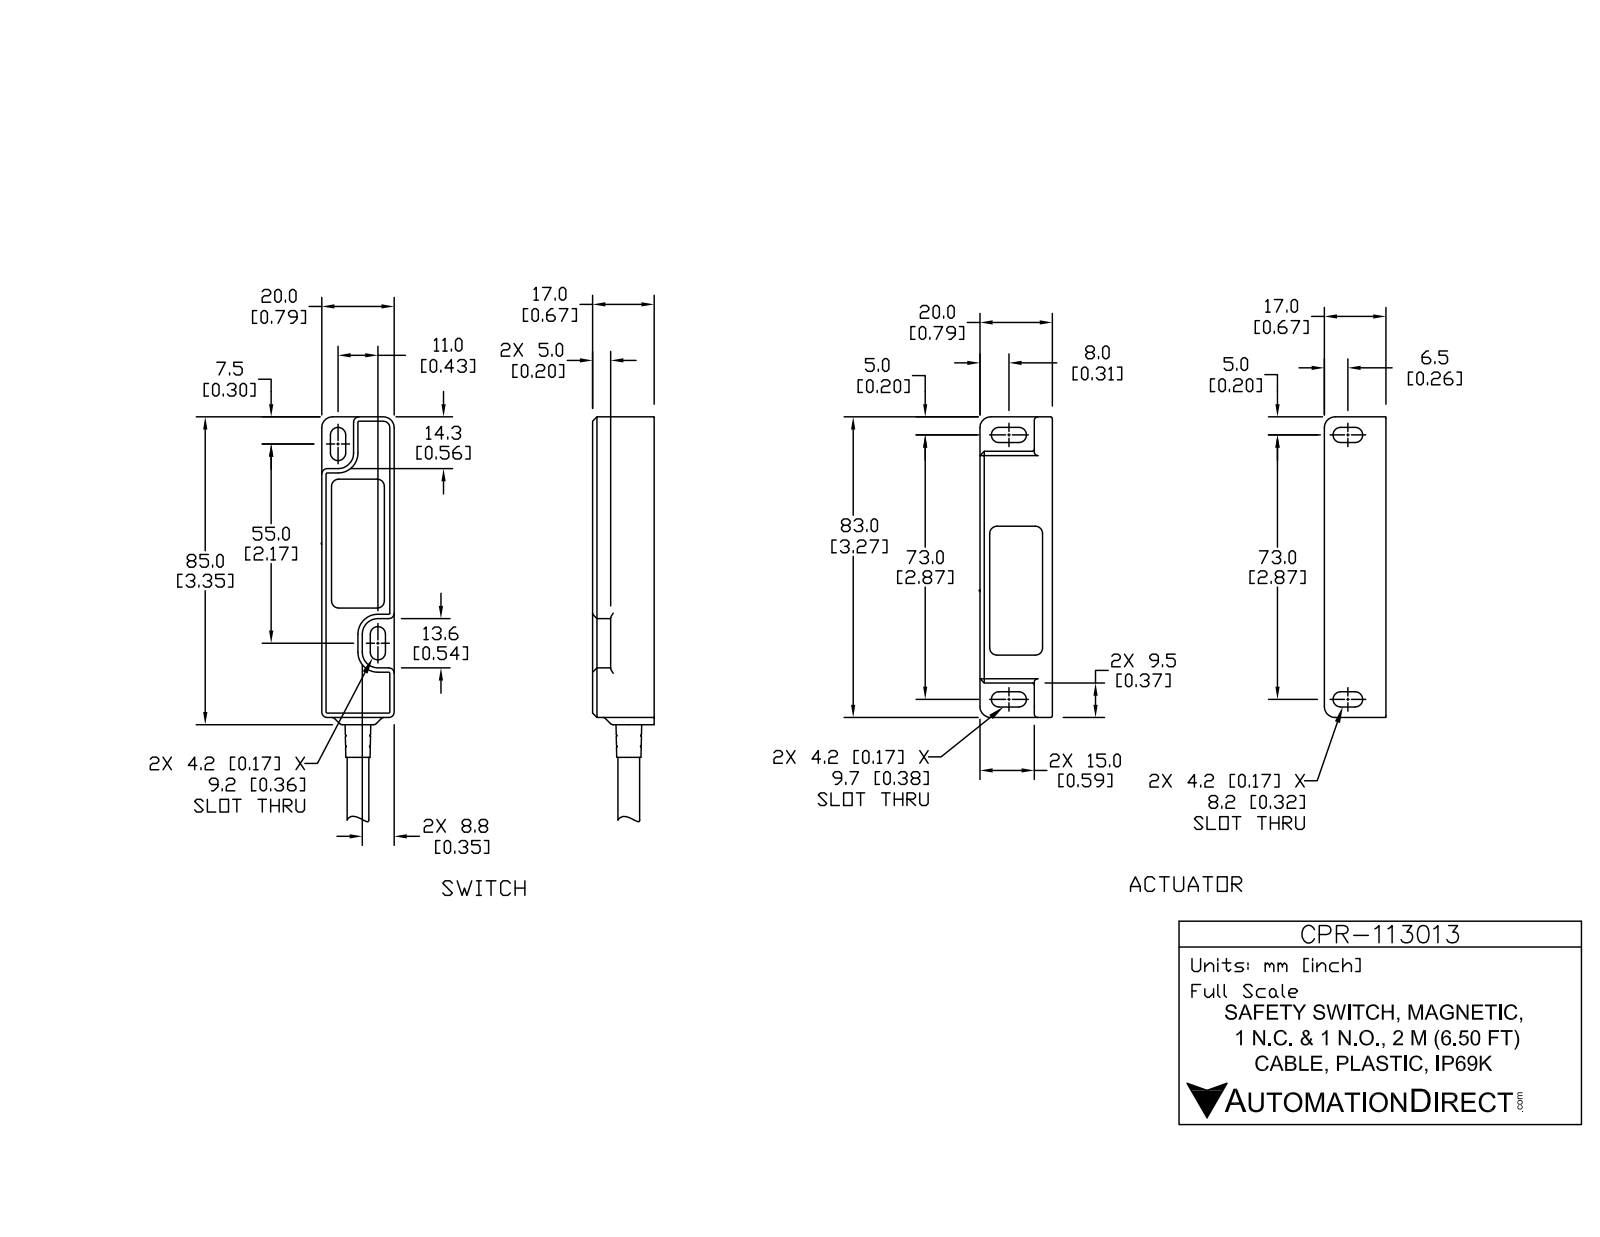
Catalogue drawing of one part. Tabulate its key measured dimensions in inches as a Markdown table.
| quantity | value |
| --- | --- |
| part name | CPR-113013; CPR-113013_1; CPR-113013_2 |
| STEP written by | SolidWorks 2017 (AUTOMOTIVE_DESIGN) |
| units | inches |
| bodies | 4 solids, 194 faces (77 planar, 69 cylindrical, 48 other) |
| overall size | 7.169 × 1.614 × 0.669 |
| volume | 3.243 in³ |
| surface area | 25.07 in² |
| round bosses / shafts (diameter × count) | 0.236 × 1 |
| partial cylindrical surfaces (radius × count) | 0.083 × 12, 0.039 × 10, 0.02 × 8, 0.079 × 8, 0.059 × 6, 0.118 × 6, 0.028 × 3, 0.169 × 3 |
| main face-to-face distances | 0.827, 0.787, 0.669, 1.614, 0.657, 0.039, 0.197, 0.472, 0.374, 2.894 |
